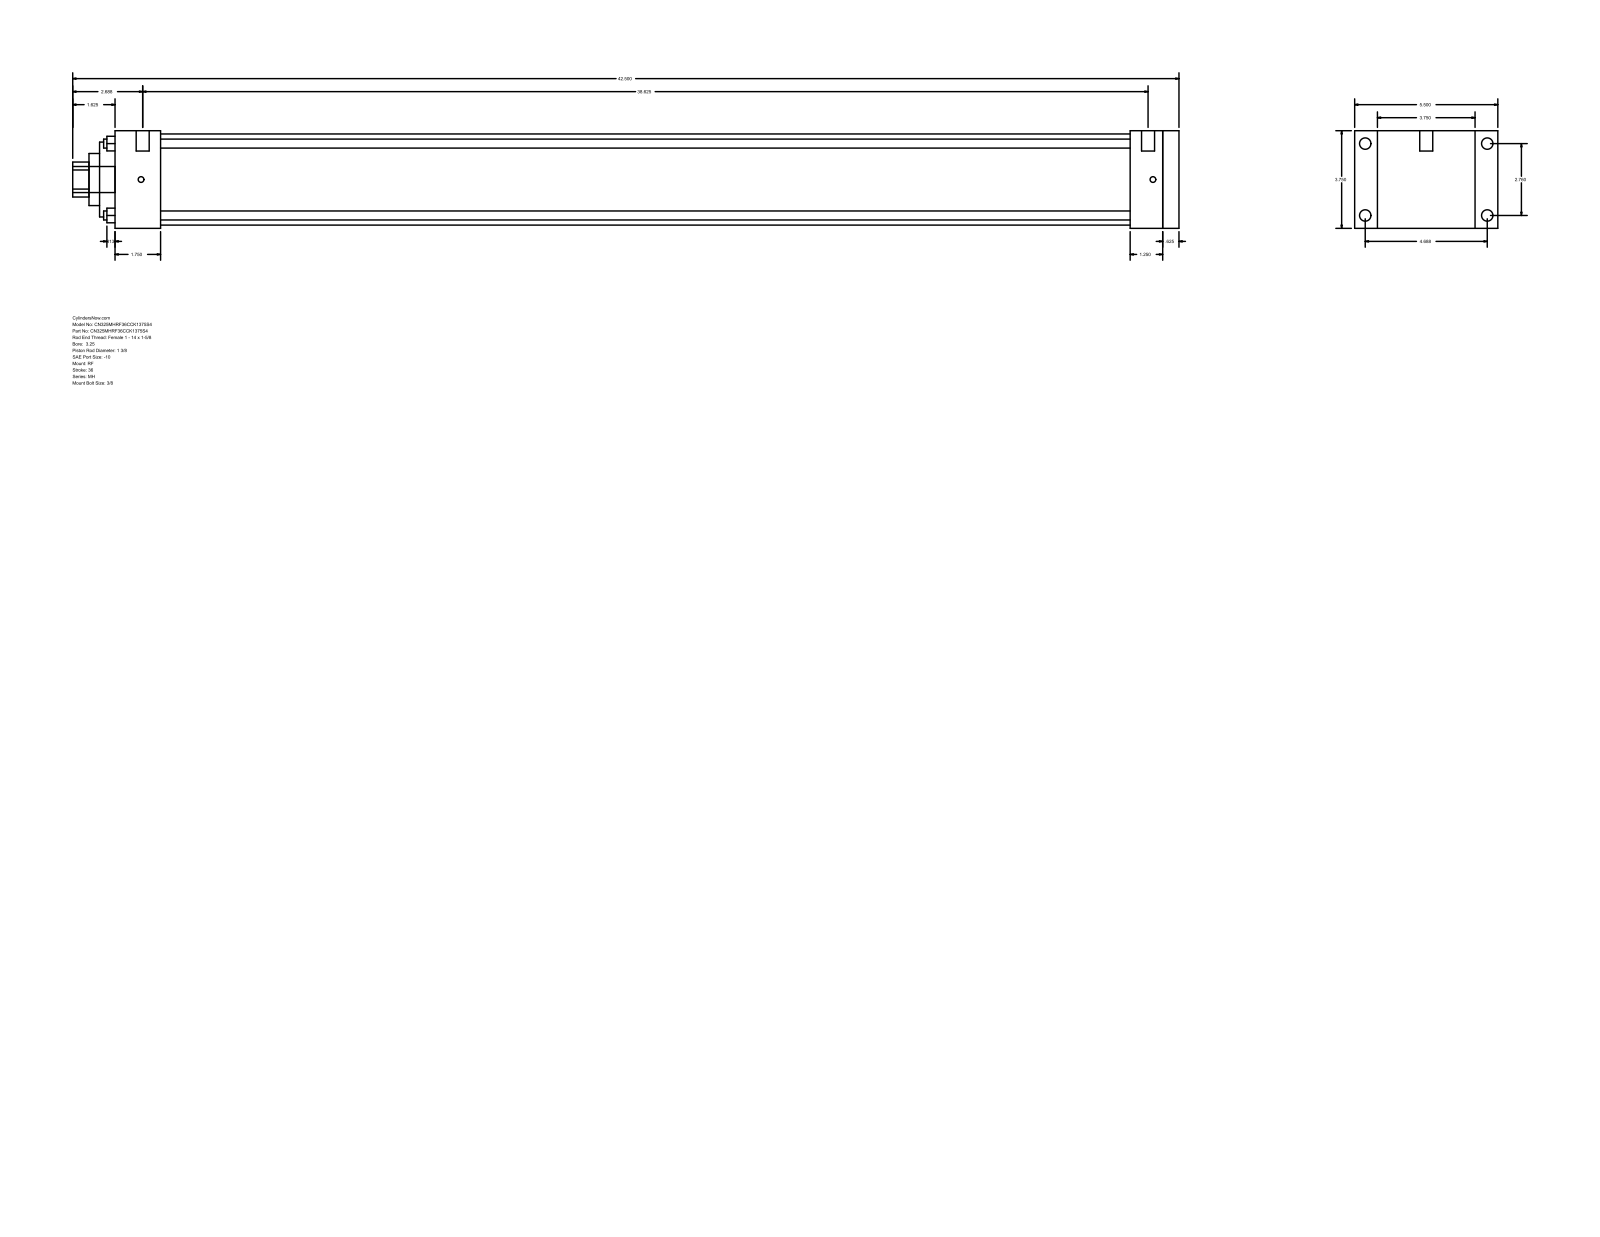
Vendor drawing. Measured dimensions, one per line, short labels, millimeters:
name: MH_RF__0325_1.375
written by: GSSL Pune (CONFIG_CONTROL_DESIGN)
unit: mm
bodies: 0 solids, 94 faces (65 planar, 29 cylindrical, 0 other)
size: 1079.5 × 139.7 × 95.25
holes: 4× ⌀8.76, 1× ⌀34.92, 1× ⌀50.8, 1× ⌀73.03, 1× ⌀88.9
bosses: 4× ⌀11.13, 4× ⌀5.56, 2× ⌀12.7, 1× ⌀25.4
rounds: 1× R17.06
face distances: 95.24, 1038.23, 15.88, 1022.35, 22.23, 117.47, 44.45, 977.9, 993.78, 990.61
hole spacings: 49.57, 70.1, 99.14
